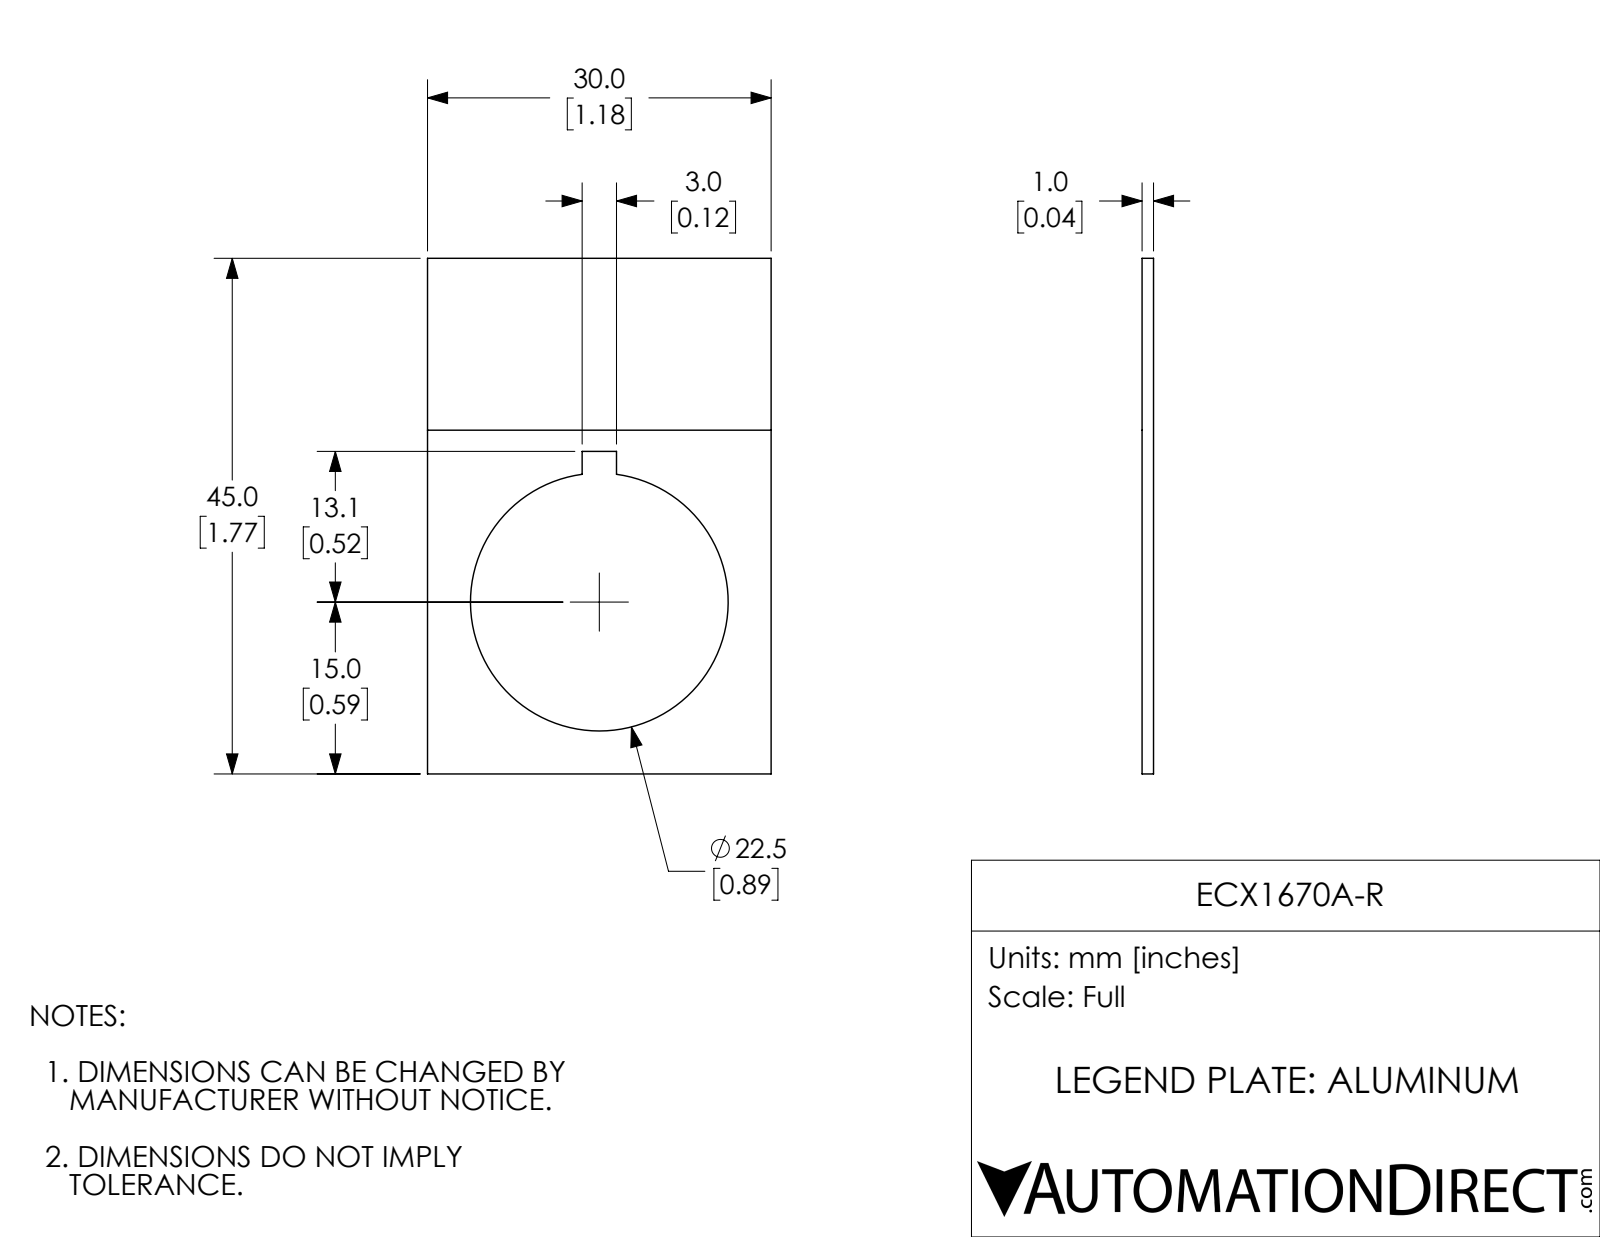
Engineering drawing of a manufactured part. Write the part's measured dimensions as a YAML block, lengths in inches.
part_name: "ECX1670A-R"
step_written_by: "SolidWorks 2017 (AUTOMOTIVE_DESIGN)"
units: inches
bodies: {solids: 1, faces: 13, planar: 10, cylindrical: 3, other: 0}
overall_size: [1.772, 1.181, 0.039]
volume: 0.058
surface_area: 3.283
round_holes:
  - {diameter: 0.886, count: 1}
face_to_face_distances: [0.039, 1.181, 1.772, 0.531, 0.65, 1.108, 0.663, 0.118]
